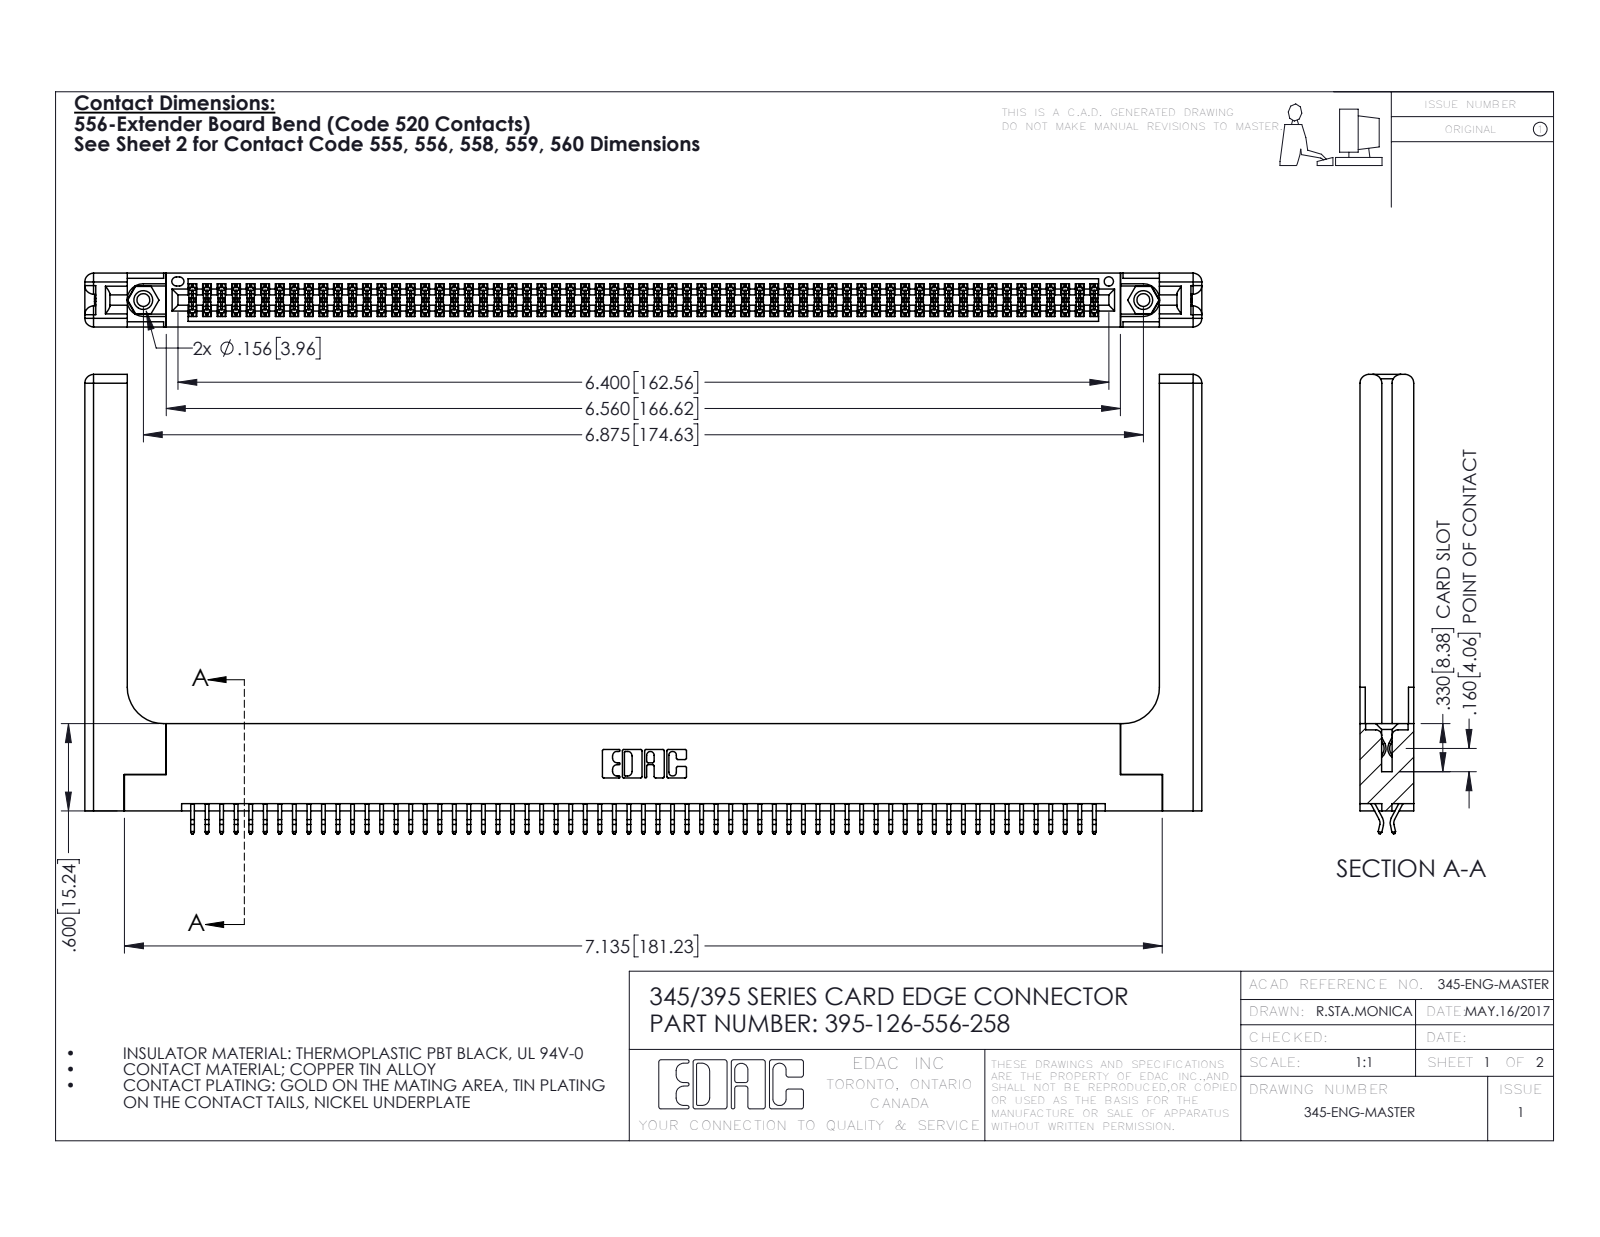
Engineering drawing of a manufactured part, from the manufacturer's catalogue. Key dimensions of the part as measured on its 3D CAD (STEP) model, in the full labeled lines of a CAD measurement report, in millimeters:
Part name (STEP PRODUCT): 345-220-058_345-220-058; 345-292-001_556 Tail; 395-126-556-258; 345-250-001_345-250-001-102 (+1 more)
STEP written by: SolidWorks 2016 (CONFIG_CONTROL_DESIGN)
Units: millimetres
Bodies: 131 solids, 7438 faces (4890 planar, 2488 cylindrical, 60 other)
Overall size (bounding box): 195 × 80.2 × 9.4
Volume: 27 610 mm³ · Surface area: 33 650 mm²
Round holes (diameter × count): ⌀2.3 ×2, ⌀3.2 ×2, ⌀4 ×2, ⌀1.6 ×1
Round bosses / shafts (diameter × count): ⌀3.9 ×2
Partial cylindrical surfaces — rounded edges, fillets, slot ends (radius × count): R0.2 ×189, R0.3 ×22, R1.5 ×16, R0.2 ×6, R0.8 ×6, R0.7 ×3, R0.3 ×2, R0.4 ×2
Main face-to-face distances: 1.8, 7.6, 9.4, 5.1, 0.6, 2.5, 6.9, 5.7, 3.8, 3.8
Hole centre spacings: 6.9, 168.6, 174.6
